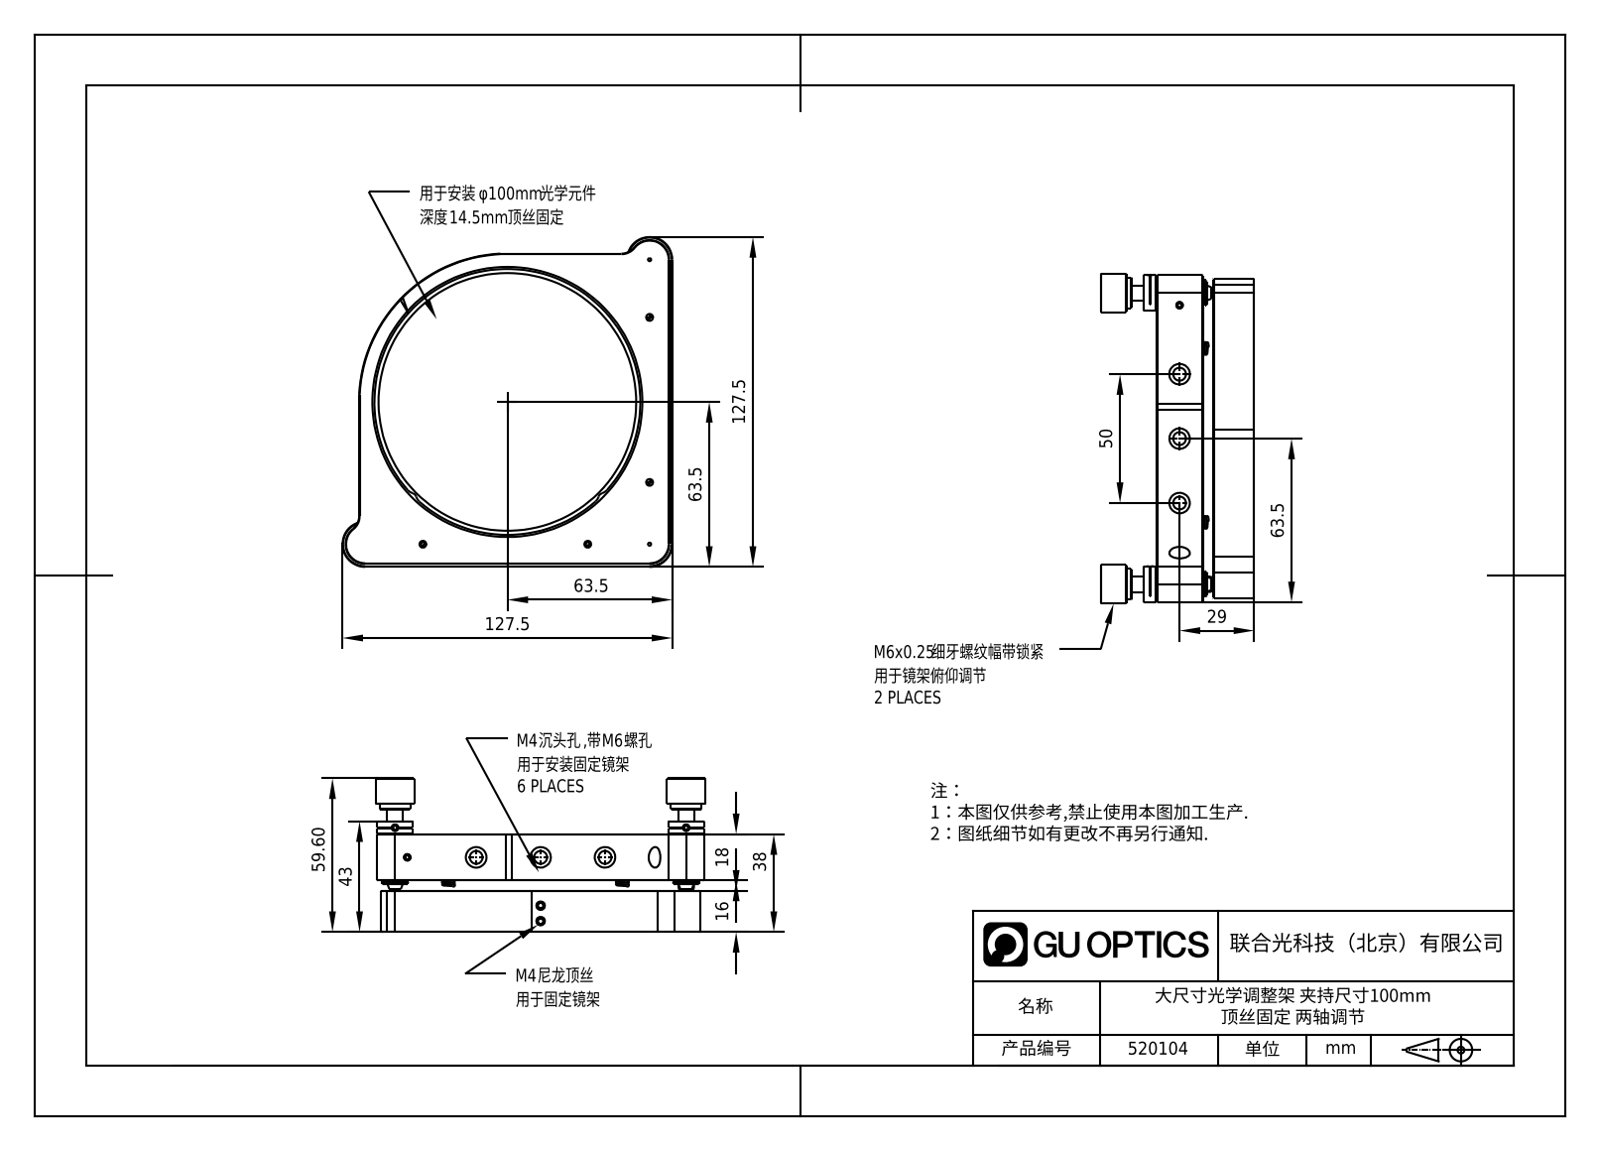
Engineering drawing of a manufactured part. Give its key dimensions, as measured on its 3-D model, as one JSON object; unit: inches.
{"part_name": "520104", "step_written_by": "SolidWorks 2020 (CONFIG_CONTROL_DESIGN)", "units": "inches", "bodies": {"solids": 0, "faces": 307, "planar": 151, "cylindrical": 84, "other": 72}, "overall_size": [5.039, 5.039, 2.35], "round_holes": [[0.197, 6], [0.315, 6], [0.256, 4], [0.374, 3], [0.098, 2], [0.047, 1], [0.394, 1]], "round_bosses_or_shafts": [[0.13, 6], [0.118, 4], [0.079, 4], [0.591, 2], [0.551, 2], [0.236, 2], [4.016, 1], [3.858, 1]], "partial_cylinders_radius": [[0.197, 10], [0.041, 8], [0.217, 3], [0.098, 2], [0.315, 2], [0.394, 2], [0.008, 1], [0.276, 1]], "face_to_face_distances": [0.63, 0.059, 0.866, 1.496, 0.157, 0.709, 0.787, 4.665, 4.724, 0.551], "hole_center_spacings": [0.984, 0.846, 0.945, 1.053, 1.969, 2.037, 2.657, 3.022]}
